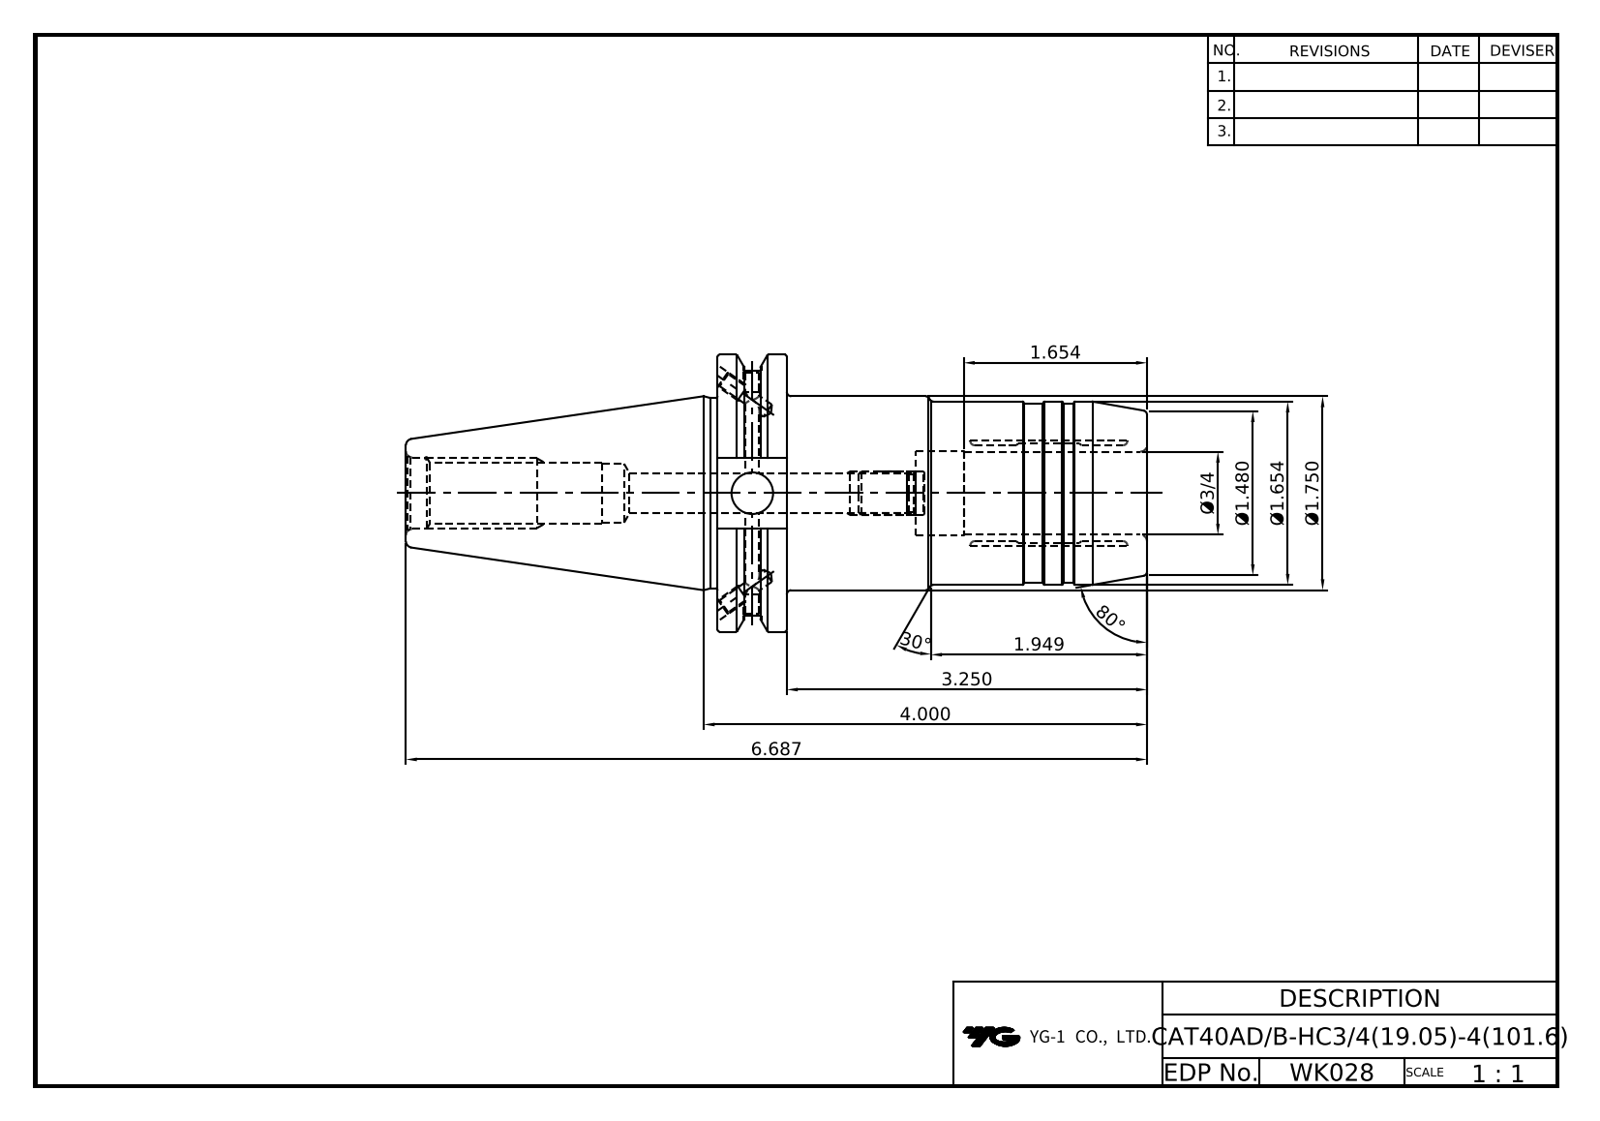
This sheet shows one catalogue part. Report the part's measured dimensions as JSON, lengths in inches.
{"part_name": "CAT40ADB-SHANK", "step_written_by": "CREO PARAMETRIC BY PTC INC, 2018500 (CONFIG_CONTROL_DESIGN)", "units": "inches", "bodies": {"solids": 1, "faces": 139, "planar": 35, "cylindrical": 34, "other": 70}, "overall_size": [6.688, 2.5, 2.395], "volume_in3": 12.47, "surface_area_in2": 56.28, "round_holes": [[0.358, 1], [0.375, 1], [0.531, 1], [0.625, 1], [0.642, 1], [0.75, 1], [0.764, 1]], "round_bosses_or_shafts": [[2.5, 1], [2.217, 1], [1.75, 1], [1.717, 1], [1.654, 1], [1.614, 1]], "face_to_face_distances": [0.626, 3.876, 3.25, 1.789, 1.163, 2.087, 1.874, 2.812, 3.438, 4.601]}
